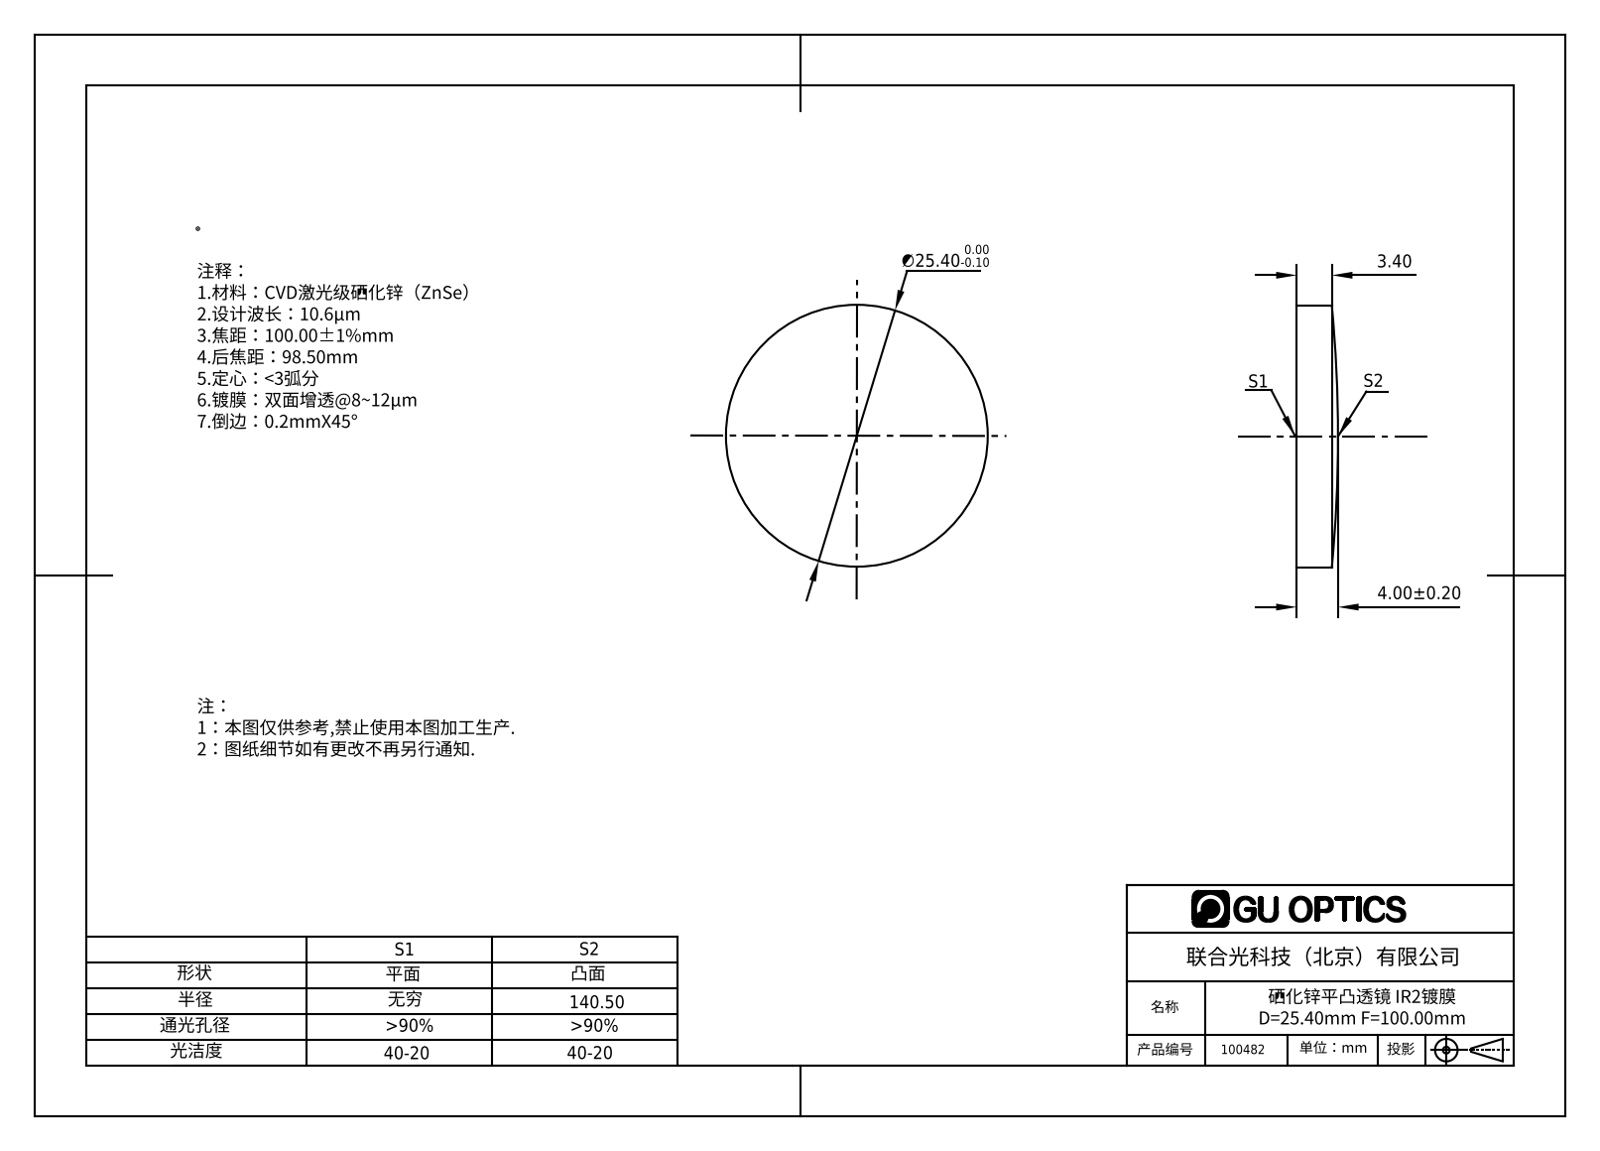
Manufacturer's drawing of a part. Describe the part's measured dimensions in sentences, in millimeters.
The part is named "100470". Its 3-D file was written by "SolidWorks 2016 (AUTOMOTIVE_DESIGN)". It is 1 solid with 5 faces: 1 planar, 2 cylindrical and 2 other. Overall it measures 25.4 by 25.4 by 4 millimeters. Its volume is 1 824 cubic millimeters and its surface area 1 271 square millimeters. Round bosses or shafts: 1 of diameter 25.4.
